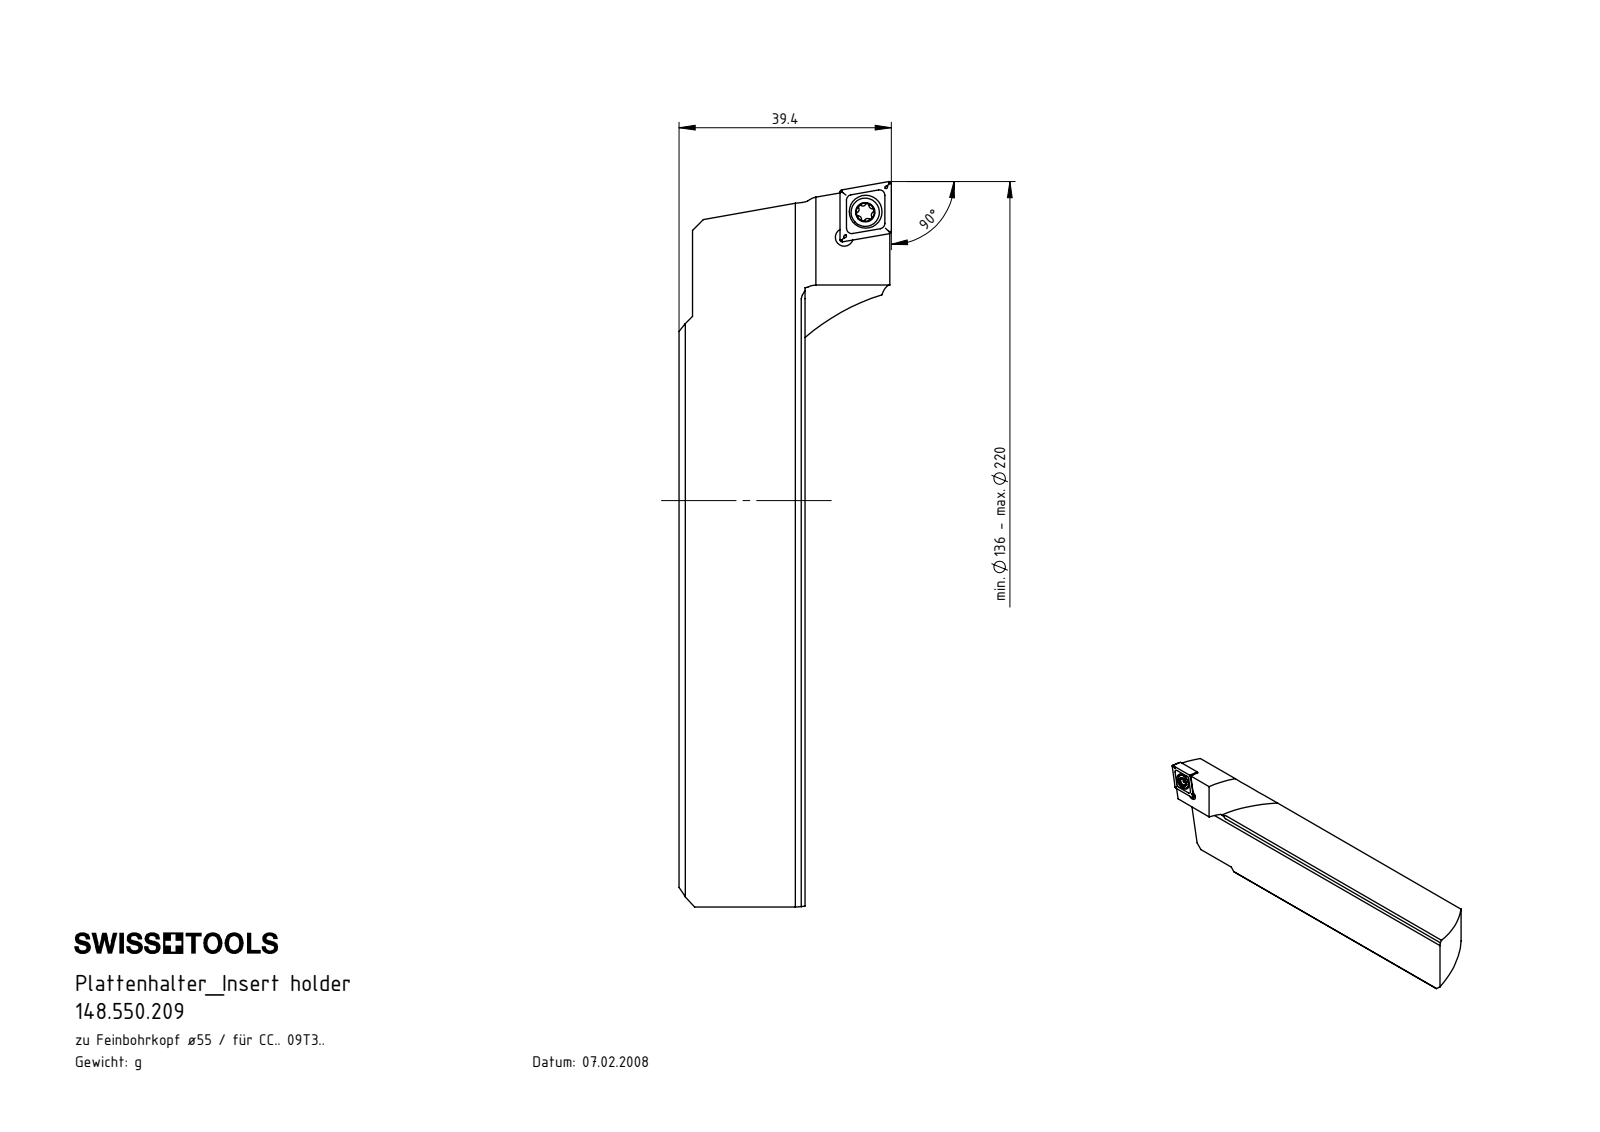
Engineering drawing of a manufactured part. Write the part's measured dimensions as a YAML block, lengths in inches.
part_name: "CCMT09T304; WCB-ER2.001.009_A; F00-WCB.136.001_C; 148.550.209"
step_written_by: "SolidWorks 2017 (CONFIG_CONTROL_DESIGN)"
units: inches
bodies: {solids: 3, faces: 559, planar: 342, cylindrical: 39, other: 178}
overall_size: [5.298, 1.551, 1.077]
volume: 3.396
surface_area: 21.7
round_holes:
  - {diameter: 0.13, count: 2}
  - {diameter: 0.173, count: 1}
  - {diameter: 0.24, count: 1}
round_bosses_or_shafts:
  - {diameter: 0.207, count: 1}
  - {diameter: 0.157, count: 1}
partial_cylinders:
  - {radius: 0.008, count: 8}
  - {radius: 0.013, count: 6}
  - {radius: 0.023, count: 6}
  - {radius: 1.575, count: 3}
  - {radius: 0.031, count: 1}
face_to_face_distances: [0.094, 0.839, 0.187, 0.281, 0.375, 0.188, 0.281, 0.375, 0.469, 0.563]
hole_center_spacings: [0.239, 0.244]
